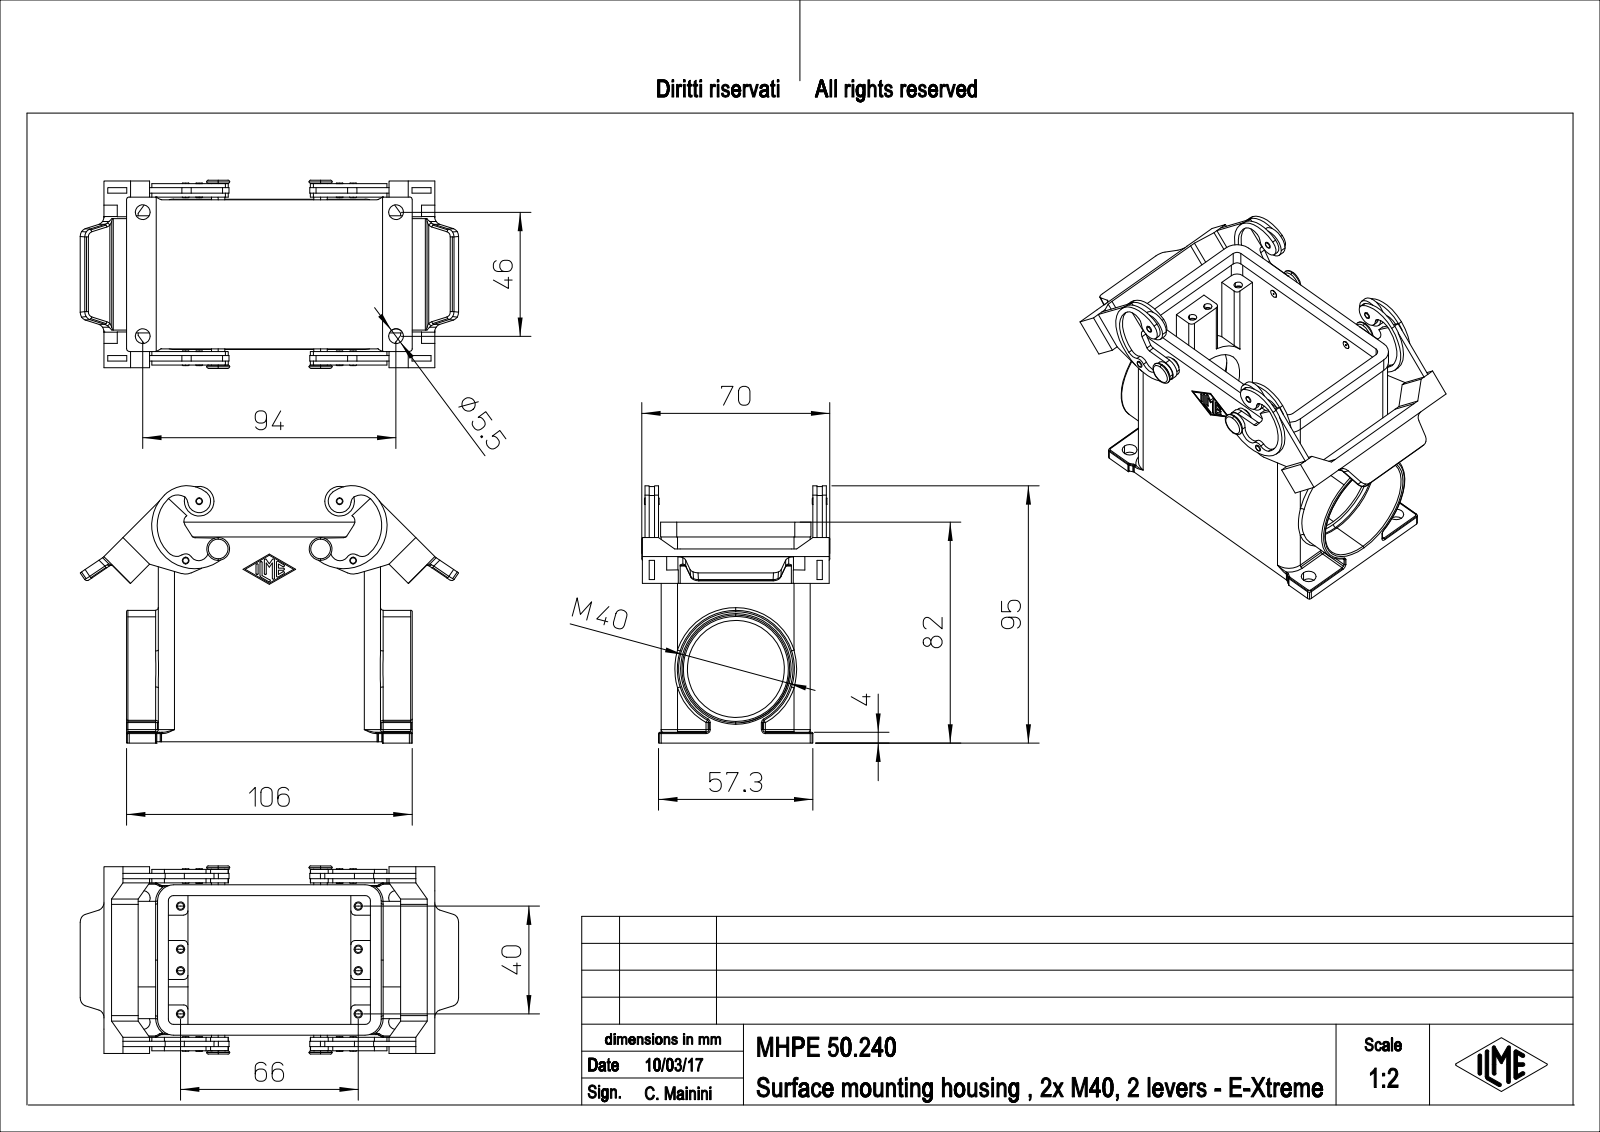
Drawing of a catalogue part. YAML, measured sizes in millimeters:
part_name: "MHPE_50.240"
step_written_by: "PTC Creo Elements/Direct Modeling 19.0E 27-Jun-2016 (C) Parametric Technology GmbH (AUTOMOTIVE_DESIGN)"
units: millimeters
bodies: {solids: 1, faces: 914, planar: 330, cylindrical: 424, other: 160}
overall_size: [140.49, 95.44, 69.8]
volume: 130175
surface_area: 75334
round_holes:
  - {diameter: 2.46, count: 8}
  - {diameter: 3.1, count: 8}
  - {diameter: 2, count: 4}
  - {diameter: 5.5, count: 4}
  - {diameter: 2.5, count: 2}
  - {diameter: 36, count: 1}
  - {diameter: 40, count: 1}
round_bosses_or_shafts:
  - {diameter: 11, count: 2}
  - {diameter: 5, count: 2}
  - {diameter: 3, count: 2}
  - {diameter: 43.5, count: 1}
partial_cylinders:
  - {radius: 1, count: 30}
  - {radius: 0.38, count: 14}
  - {radius: 0.5, count: 14}
  - {radius: 3, count: 12}
  - {radius: 1.5, count: 10}
  - {radius: 6, count: 8}
  - {radius: 2.5, count: 6}
  - {radius: 2, count: 4}
face_to_face_distances: [3, 52.3, 3.5, 4, 55.3, 49.3, 11, 71.5, 62.3, 4.5]
hole_center_spacings: [14.32, 16, 23.6, 24, 30.41, 45.22, 66, 67.91]
